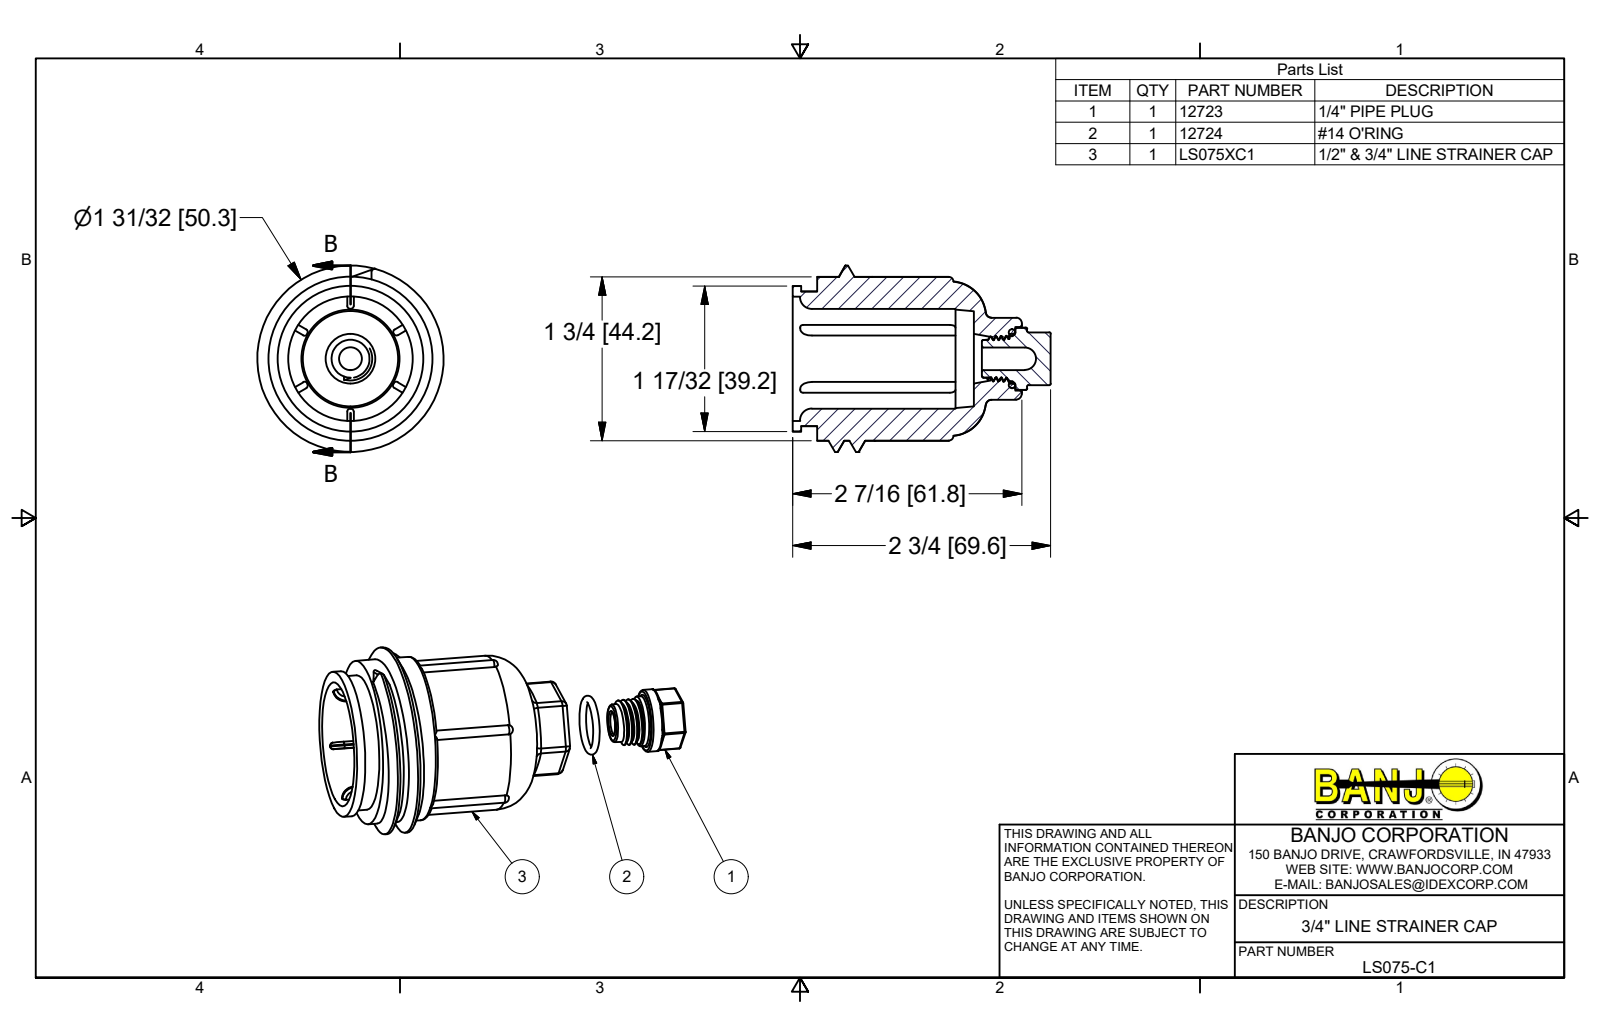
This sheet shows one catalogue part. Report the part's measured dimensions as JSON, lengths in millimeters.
{"part_name": "LS075-C1; 12723; 12724; LS075XC1", "step_written_by": "Autodesk Inventor 2018 (AUTOMOTIVE_DESIGN)", "units": "millimeters", "bodies": {"solids": 3, "faces": 303, "planar": 62, "cylindrical": 100, "other": 141}, "overall_size": [182, 50.3, 50.3], "volume_mm3": 41280, "surface_area_mm2": 26900, "round_holes": [[6.1, 1], [17.1, 1], [33.5, 1]], "round_bosses_or_shafts": [[50.3, 1], [44.2, 1], [41.7, 1], [39.2, 1], [36.3, 1], [16.8, 1], [13.5, 1]], "partial_cylinders_radius": [[0.4, 18], [0.8, 18], [1.5, 12], [1.3, 6], [3.2, 6]], "face_to_face_distances": [1.8, 42.3, 6.6, 48.9, 22.1, 3.9, 18.2, 2.3, 4.3, 46.6]}
